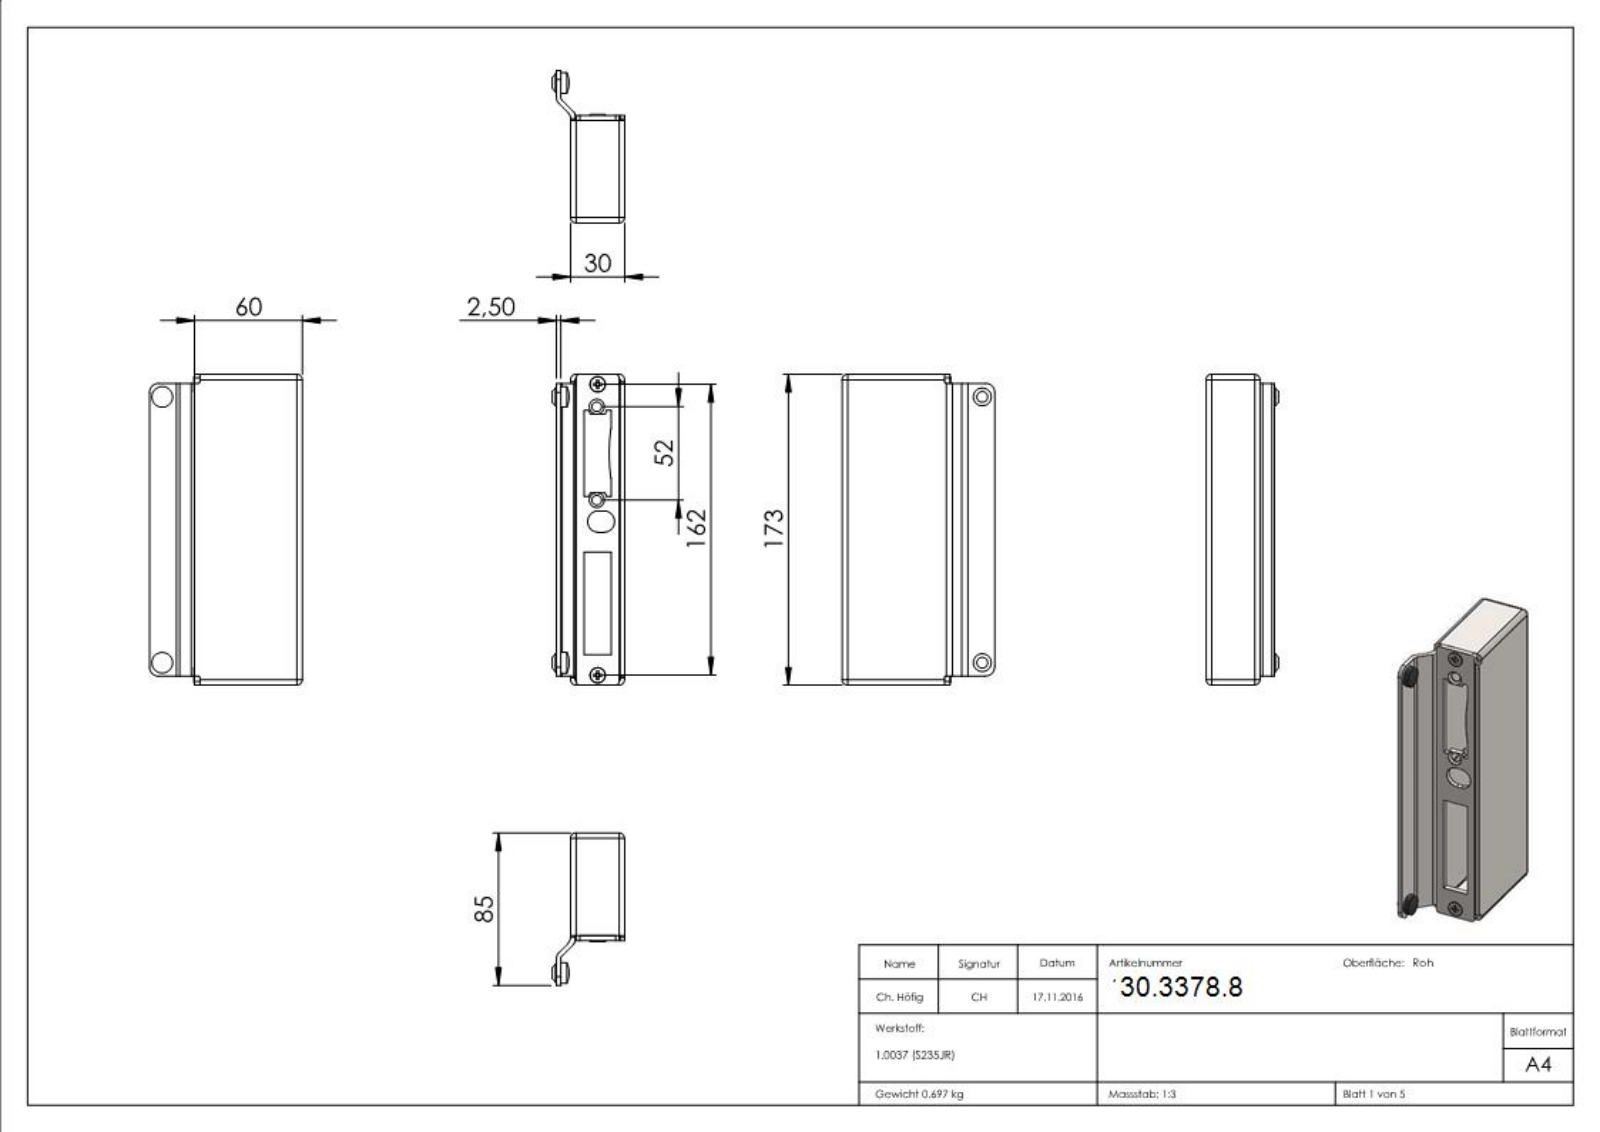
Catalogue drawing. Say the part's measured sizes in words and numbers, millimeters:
The part is named "14746 Teil3; countersunk flat head cross recess screw_din_ISO 7046-1 - M4 x 8 - Z --- 8S; 14746 Teil1; 14746 Teil2 (+2 more)". Its 3-D file was written by "SolidWorks 2018 (CONFIG_CONTROL_DESIGN)". It is 6 solids with 409 faces: 211 planar, 77 cylindrical and 121 other. Overall it measures 173 by 85 by 40.3 millimeters. Its volume is 90 702 cubic millimeters and its surface area 74 317 square millimeters. Round holes: 2 of diameter 3.3, 2 of diameter 5.4, 2 of diameter 7. Round bosses or shafts: 2 of diameter 11.5, 2 of diameter 10, 2 of diameter 8.4, 2 of diameter 6, 2 of diameter 4. Partial cylindrical surfaces (rounded edges, fillets, slot ends): 12 of radius 0.2, 8 of radius 0.5, 8 of radius 3, 6 of radius 2, 4 of radius 5, 2 of radius 1, 2 of radius 2.5, 2 of radius 6. The main face-to-face distances are 2.5, 27.5, 25, 30, 8, 35.5, 3, 57.5, 57, 60. The hole center spacings are 12.51, 52, 64.5, 97.5, 148, 149.5, 162.
